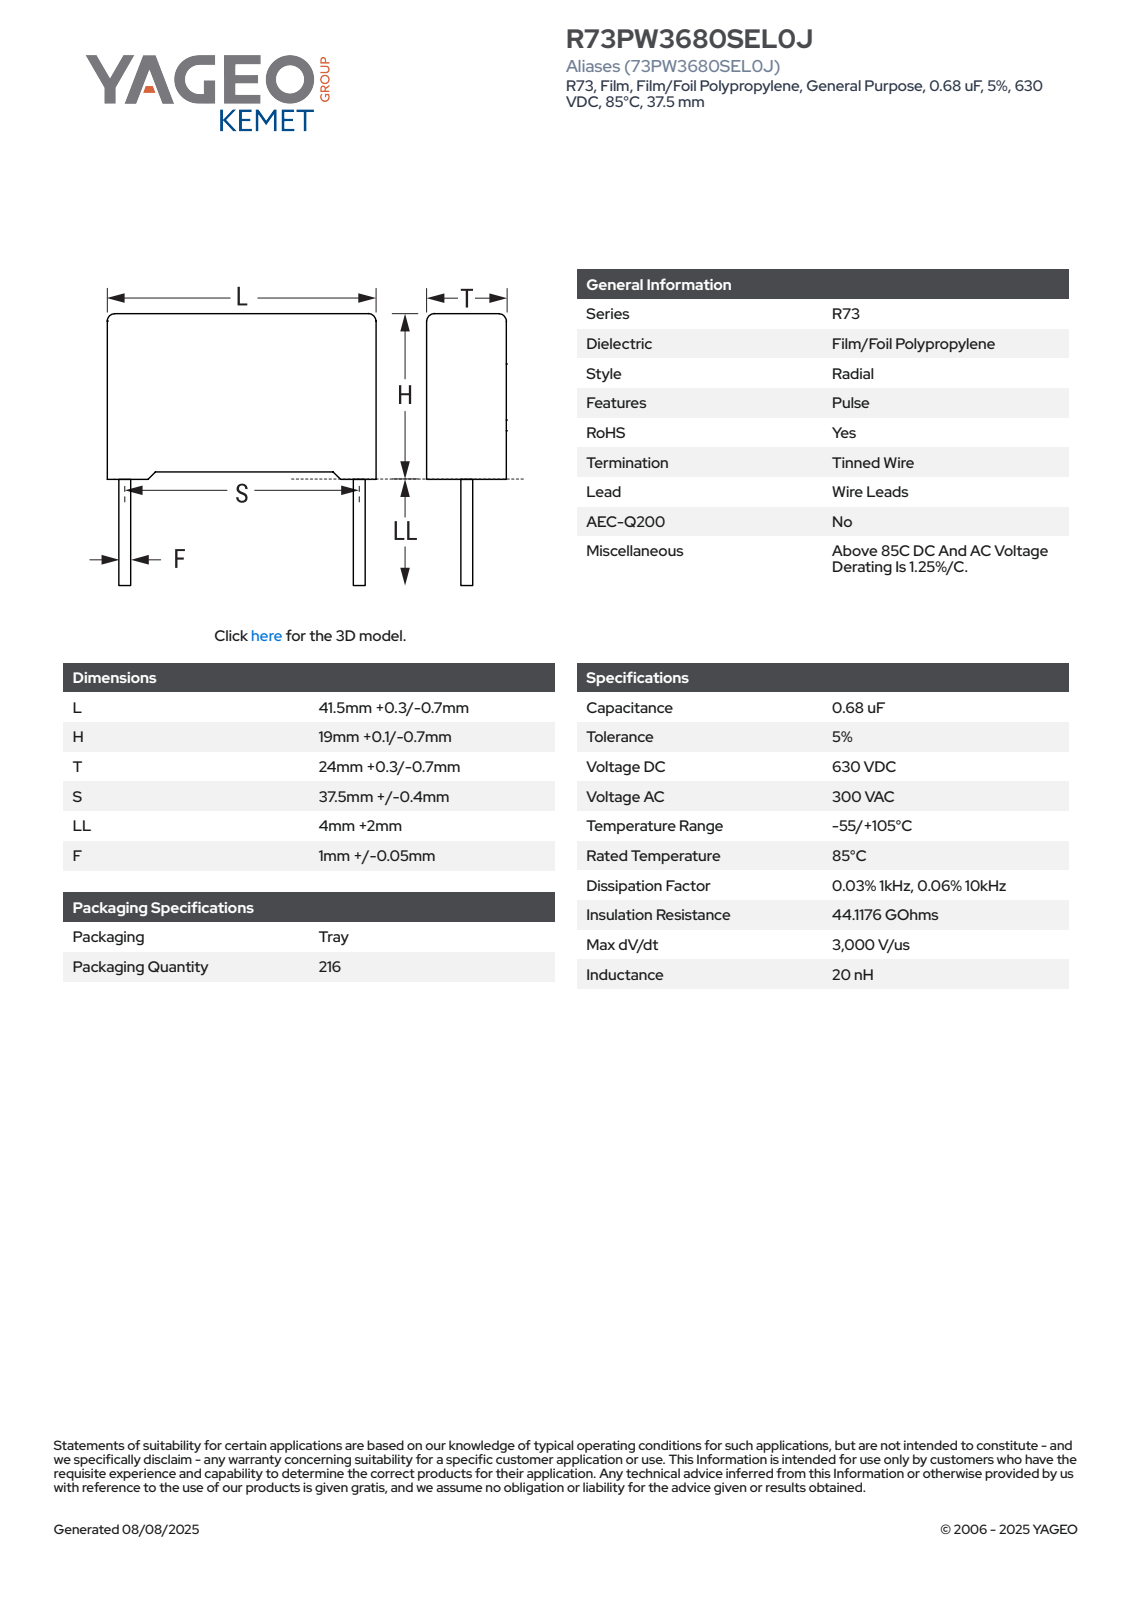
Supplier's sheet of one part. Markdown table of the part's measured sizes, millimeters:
| quantity | value |
| --- | --- |
| part name | CFR_RB2_41.5X19X24_L41.8H19.1T24.3S37.5LL6F1.05 |
| STEP written by | SolidWorks 2021 (AUTOMOTIVE_DESIGN) |
| units | millimeters |
| bodies | 4 solids, 85 faces (77 planar, 8 cylindrical, 0 other) |
| overall size | 41.8 × 25.1 × 24.3 |
| volume | 18 715 mm³ |
| surface area | 4 707 mm² |
| round bosses / shafts (diameter × count) | 1.05 × 2 |
| partial cylindrical surfaces (radius × count) | 0.5 × 4 |
| main face-to-face distances | 18.35, 24.3, 41.8, 18.44, 0.66, 0.75, 19.1, 1.39, 40.41, 24.31 |
